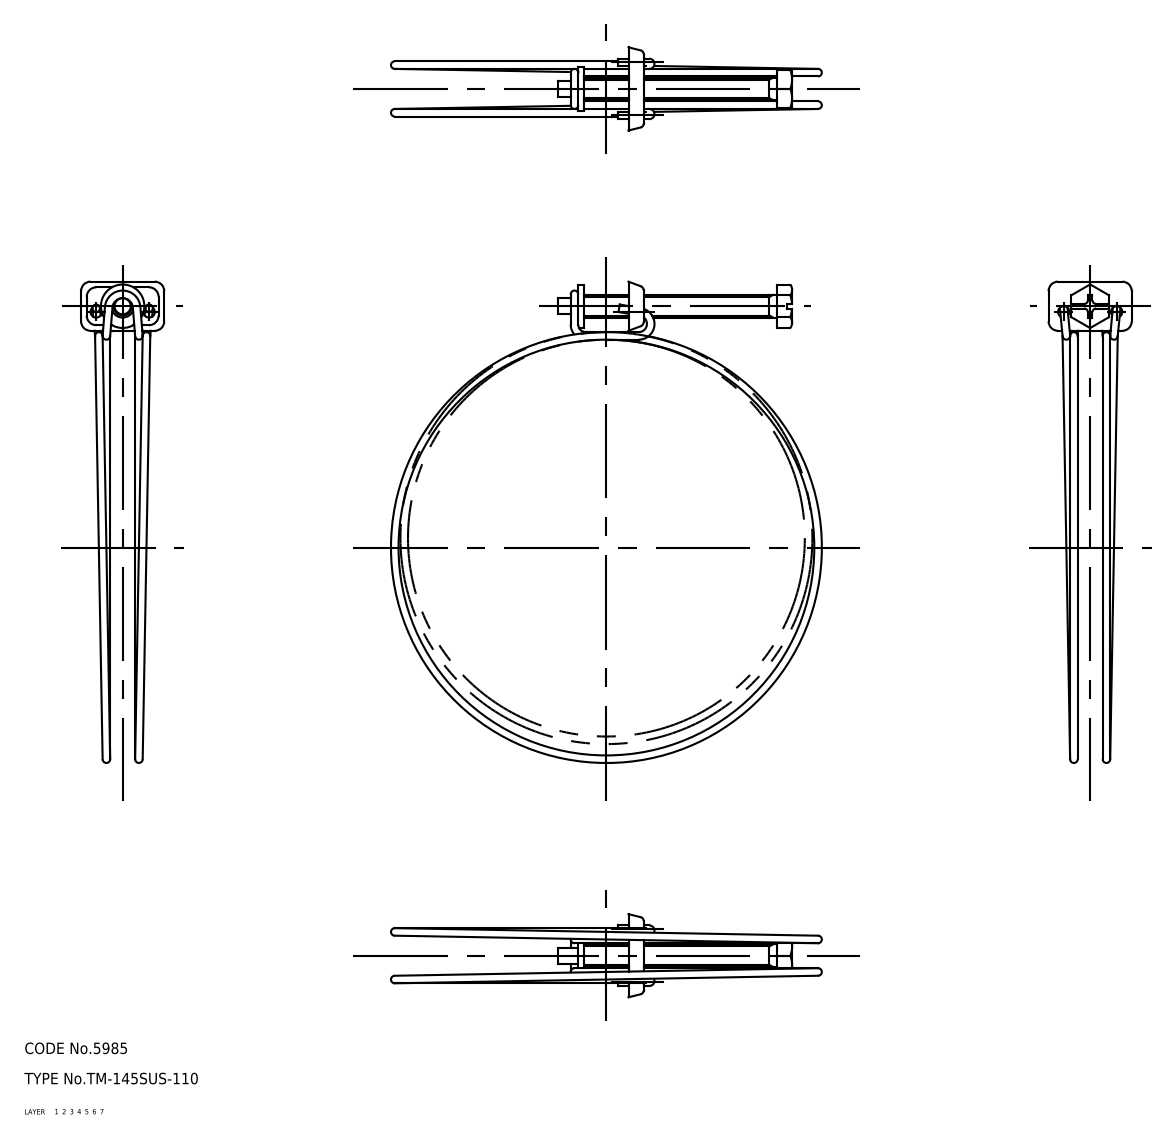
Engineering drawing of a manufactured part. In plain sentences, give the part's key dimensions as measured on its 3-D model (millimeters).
The part is named "screw; holder; band; TM_145SUS_110_21132_36". Its 3-D file was written by "CADfix (AUTOMOTIVE_DESIGN)". It is 3 solids with 119 faces: 0 planar, 0 cylindrical and 119 other. Overall it measures 127.35 by 114 by 22 millimeters. Its volume is 4 985 cubic millimeters and its surface area 7 383 square millimeters.
